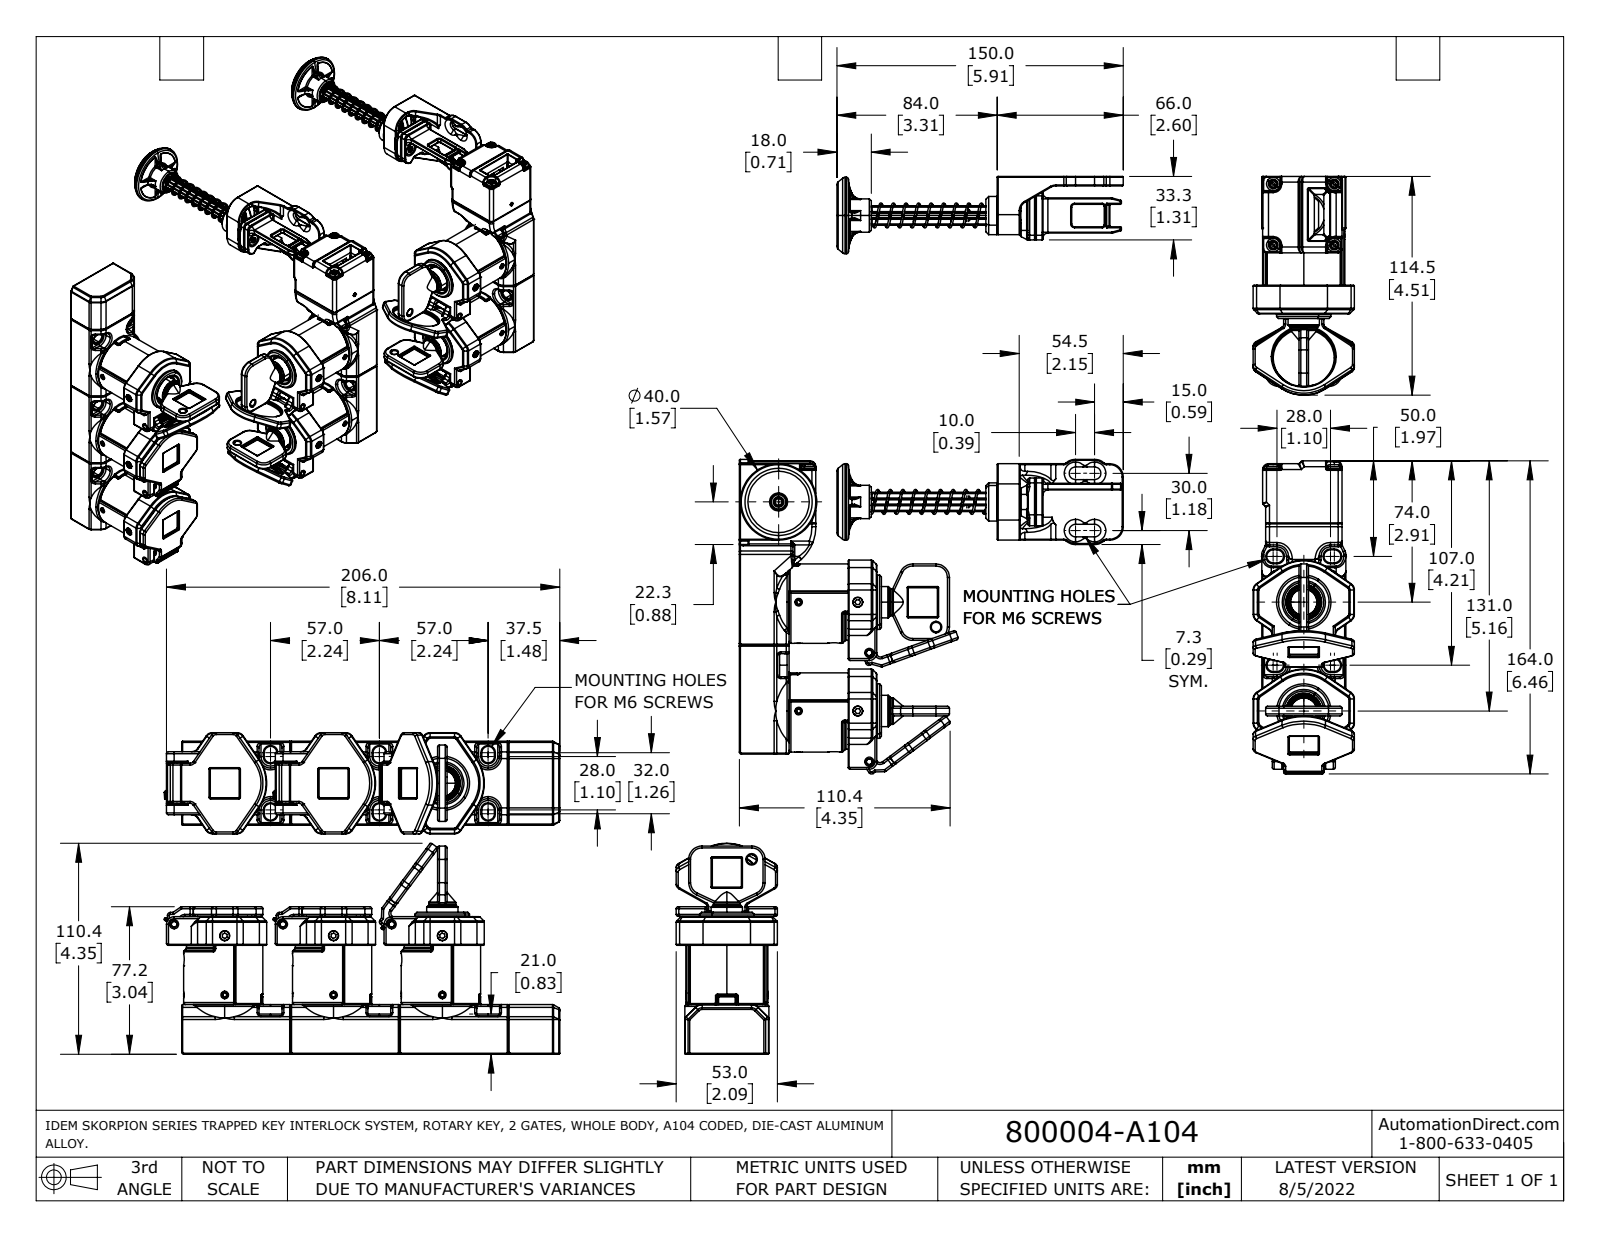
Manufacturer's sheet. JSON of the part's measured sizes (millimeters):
{"part_name": "800004-A103; 800004-A103_2; 800004-A103_3; 800004-A103_1", "step_written_by": "SolidWorks 2021 (AUTOMOTIVE_DESIGN)", "units": "millimeters", "bodies": {"solids": 6, "faces": 6863, "planar": 1536, "cylindrical": 2855, "other": 2472}, "overall_size": [267.4, 263.5, 229.2], "volume_mm3": 481600, "surface_area_mm2": 224800, "round_holes": [[4.5, 13], [3.3, 11], [4.2, 8], [8, 8], [3.5, 7], [4, 4], [5, 4], [40.8, 4], [3, 3], [7.4, 3], [1.3, 2], [2.2, 2]], "round_bosses_or_shafts": [[1.3, 14], [7.4, 8], [3.5, 8], [3.9, 6], [40, 4], [7, 4], [3.1, 4], [10, 3]], "partial_cylinders_radius": [[0.5, 921], [1, 493], [0.3, 92], [2, 72], [4, 44], [3, 28], [1.5, 26], [3.3, 20]], "face_to_face_distances": [77.2, 44, 3, 1, 5, 76.2, 57, 180.7, 224.7, 25], "hole_center_spacings": [57, 20.9, 43.8, 63.5, 114, 28, 73.8, 22.6]}
